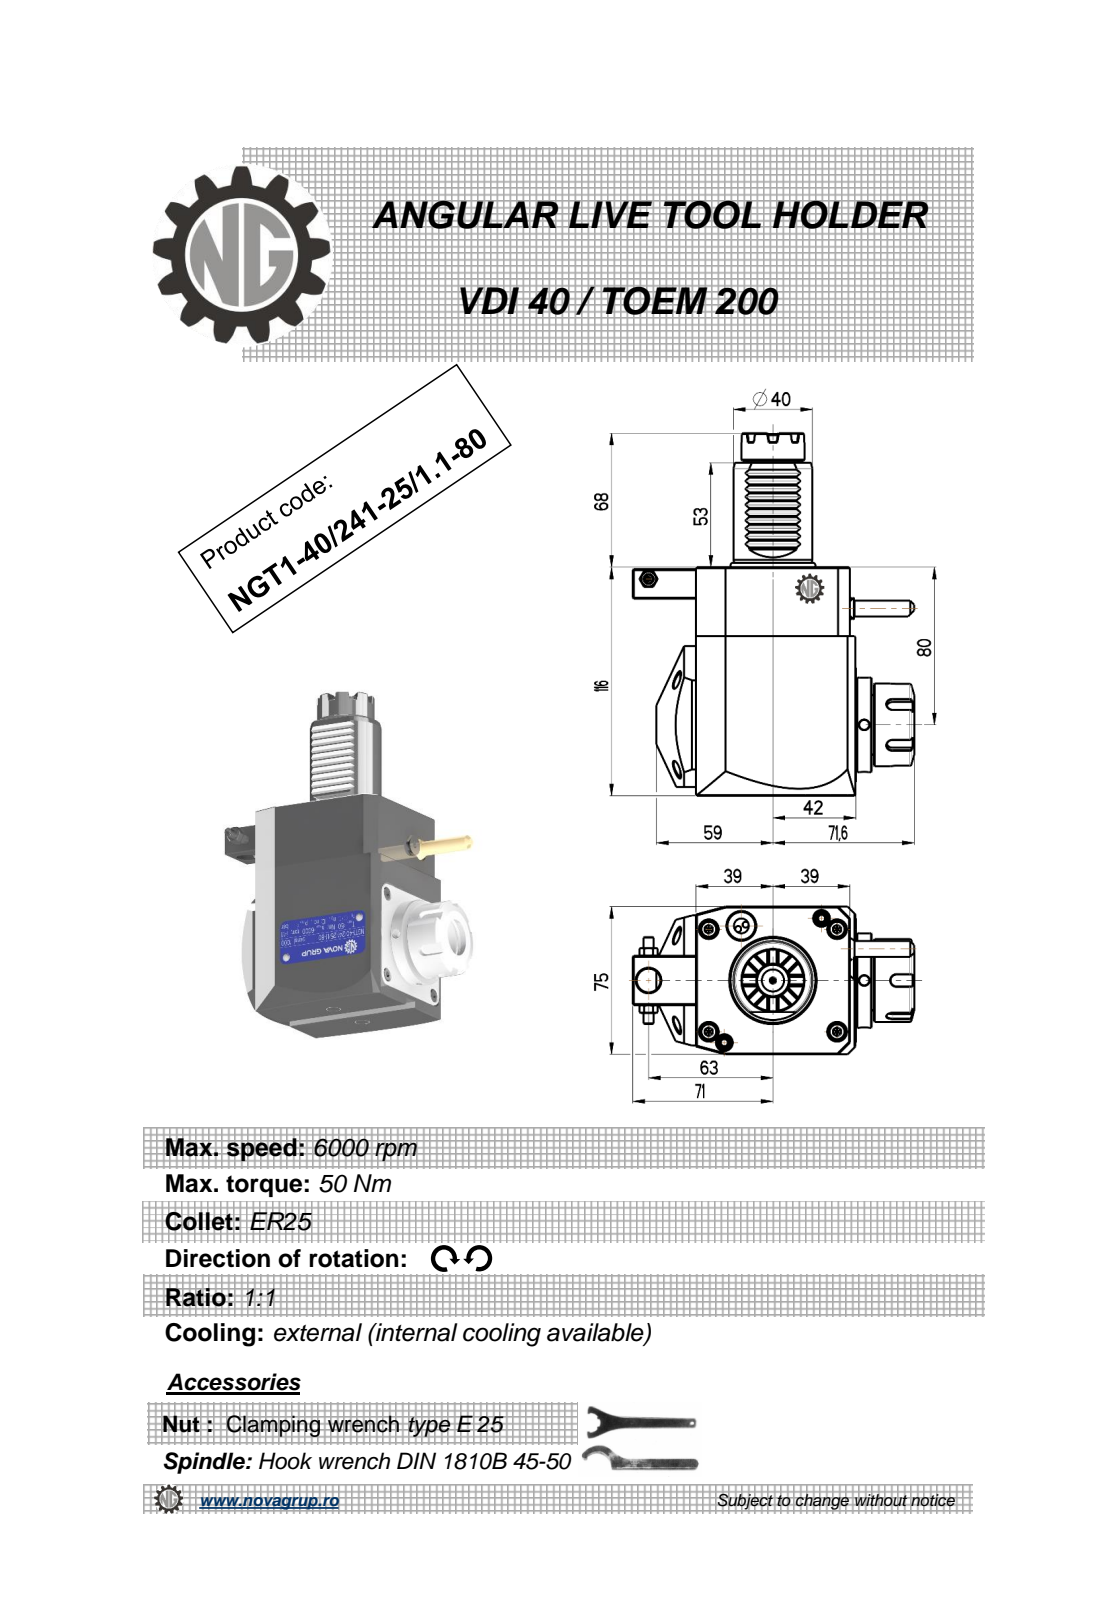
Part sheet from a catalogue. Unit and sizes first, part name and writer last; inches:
Units: inches
Overall size (bounding box): 7.244 × 5.614 × 3.016
Round holes (diameter × count): ⌀0.197 ×3, ⌀0.118 ×1, ⌀0.165 ×1, ⌀0.374 ×1, ⌀0.472 ×1, ⌀0.799 ×1
Round bosses / shafts (diameter × count): ⌀1.89 ×1, ⌀1.654 ×1, ⌀1.575 ×1, ⌀1.476 ×1, ⌀1.299 ×1, ⌀1.26 ×1, ⌀0.669 ×1, ⌀0.441 ×1
Partial cylindrical surfaces — rounded edges, fillets, slot ends (radius × count): R0.01 ×12, R0.012 ×10, R0.009 ×6, R0.118 ×5, R0.02 ×1, R0.339 ×1, R1.575 ×1
Main face-to-face distances: 2.953, 4.567, 3.189, 3.071, 0.118, 3.181, 0.11, 0.984, 0.295, 0.433
Hole centre spacings: 0.824, 2.407, 2.854, 4.301, 5.195
Volume: 52.55 in³ · Surface area: 109.9 in²
Bodies: 1 solid, 514 faces (228 planar, 97 cylindrical, 189 other)
Part name (STEP PRODUCT): NGT1_40_241_25_1_1_80
STEP written by: PRO/ENGINEER BY PARAMETRIC TECHNOLOGY CORPORATION, 2010280 (CONFIG_CONTROL_DESIGN)
